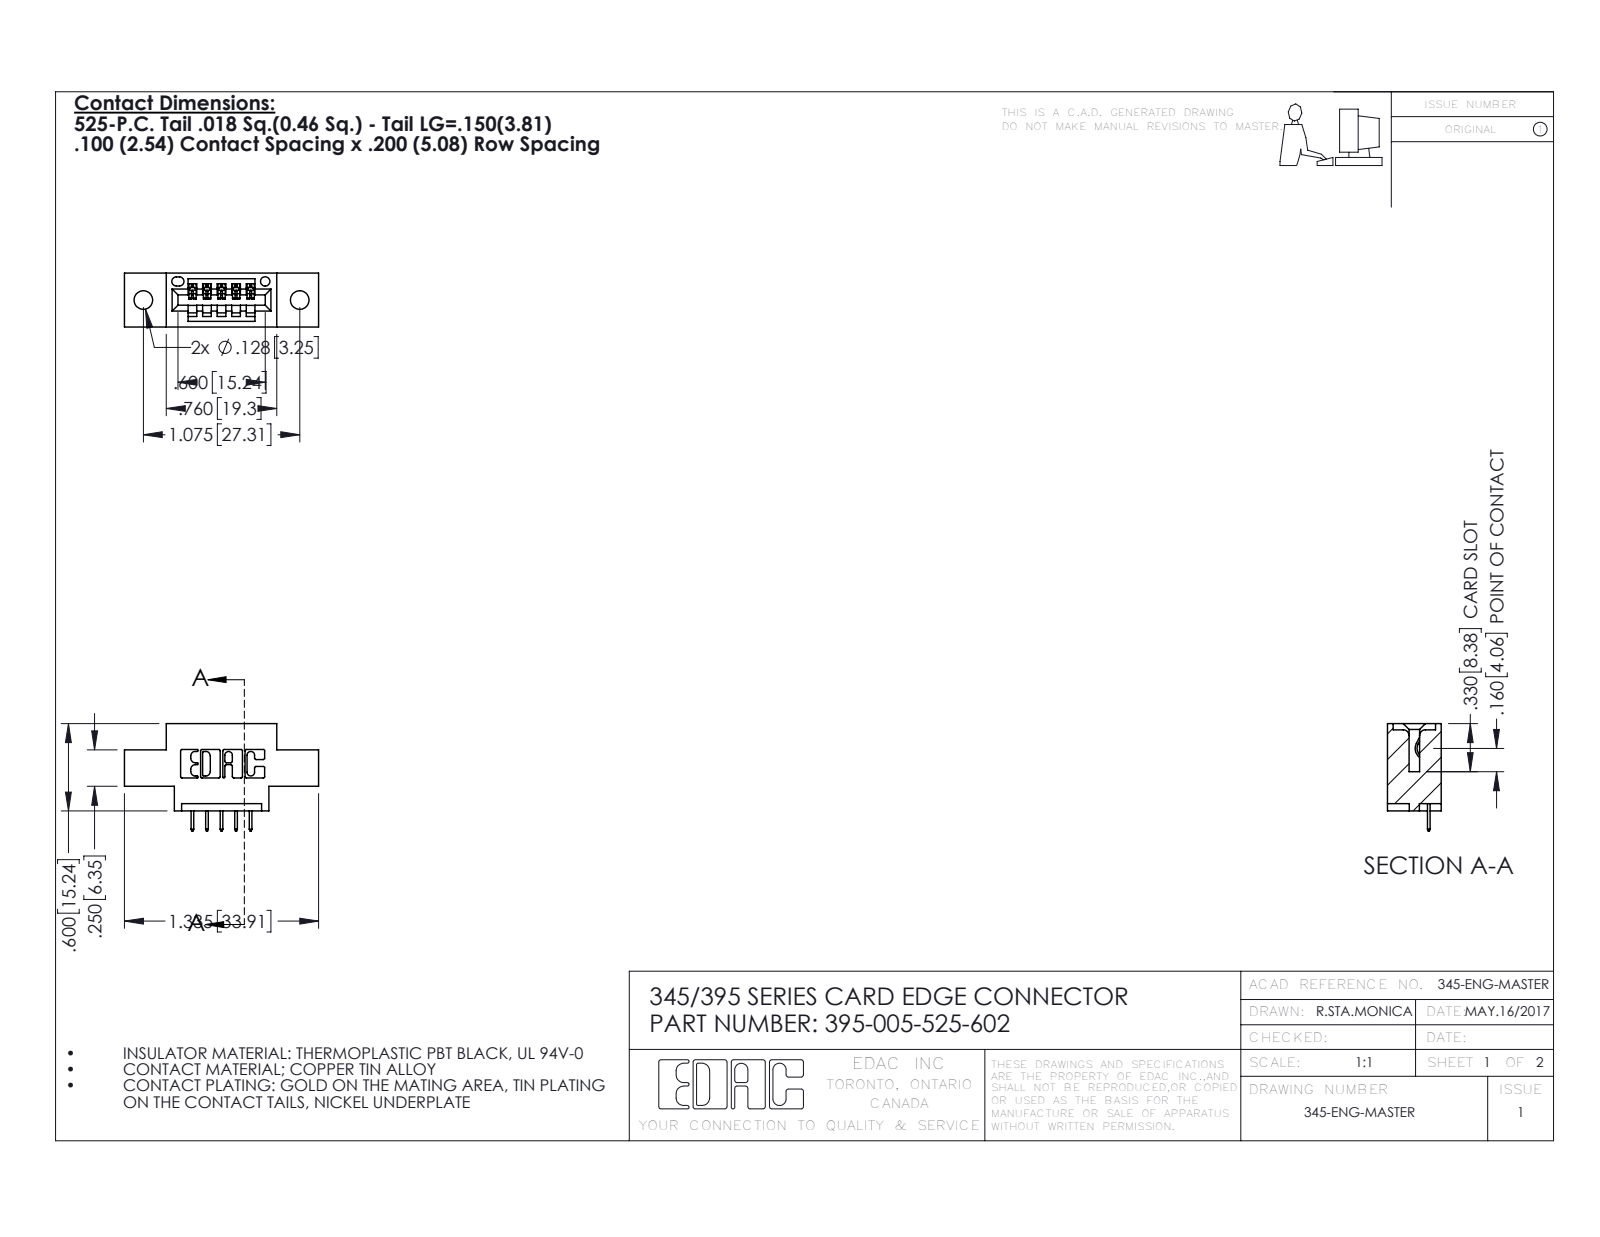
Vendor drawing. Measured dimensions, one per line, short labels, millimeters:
name: 395-005-525-602; 345-292-001_345-293-125; 345 Part_0.170 Offset - 0.128 Dia
written by: SolidWorks 2020 (CONFIG_CONTROL_DESIGN)
unit: mm
bodies: 6 solids, 440 faces (314 planar, 126 cylindrical, 0 other)
size: 33.9 × 18.7 × 9.4
volume: 2 750 mm³; area: 2 935 mm²
holes: 2× ⌀3.3, 1× ⌀1.6
rounds: 22× R0.3, 10× R0.2, 6× R0.2, 6× R0.8, 3× R0.7, 2× R0.8, 2× R1, 1× R0.4
face distances: 9.4, 5.1, 2.5, 1.8, 7.6, 6.4, 0.6, 1.5, 14, 3.8
hole spacings: 6.9, 21.5, 27.3
